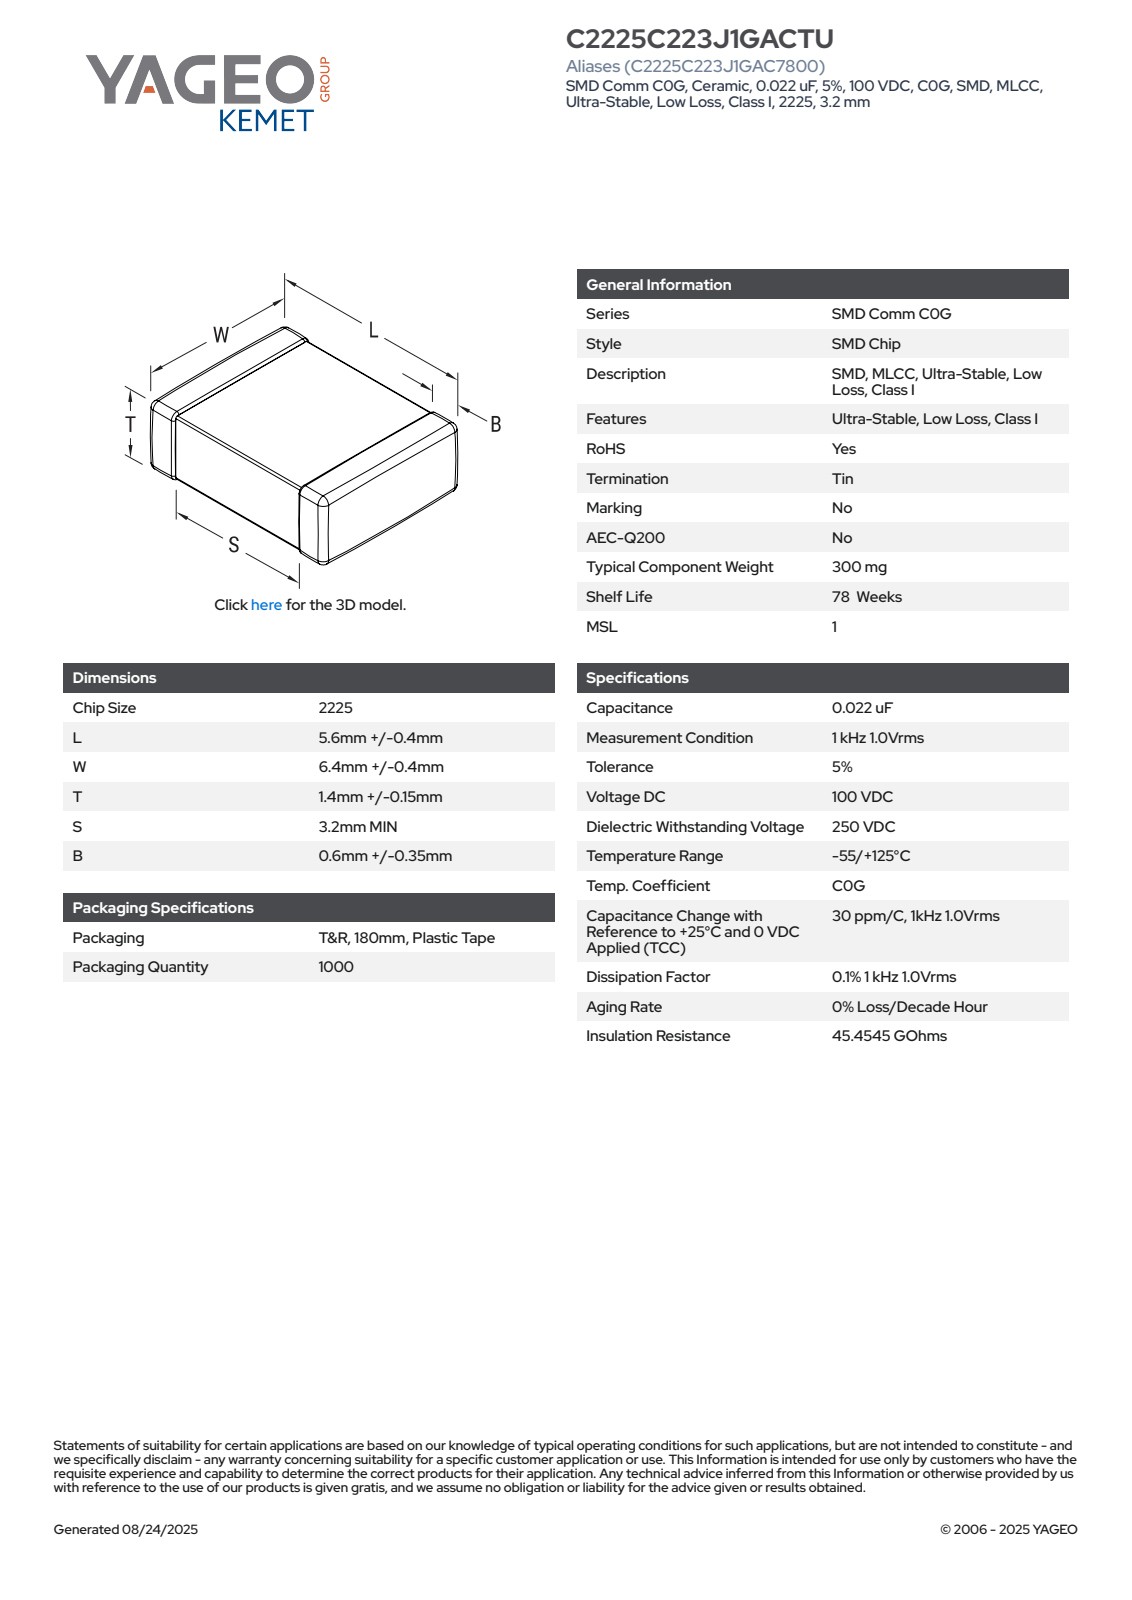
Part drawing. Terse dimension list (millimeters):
name: CCS_CCSTD_2225_L6W6.8T1.55B0.6
written by: SolidWorks 2021 (AUTOMOTIVE_DESIGN)
unit: mm
bodies: 4 solids, 125 faces (71 planar, 38 cylindrical, 16 other)
size: 6.8 × 6 × 1.55
volume: 54 mm³; area: 122 mm²
rounds: 24× R0.14
face distances: 1.27, 1.41, 1.55, 6, 6.52, 6.66, 6.8, 1, 2.24, 3.76
